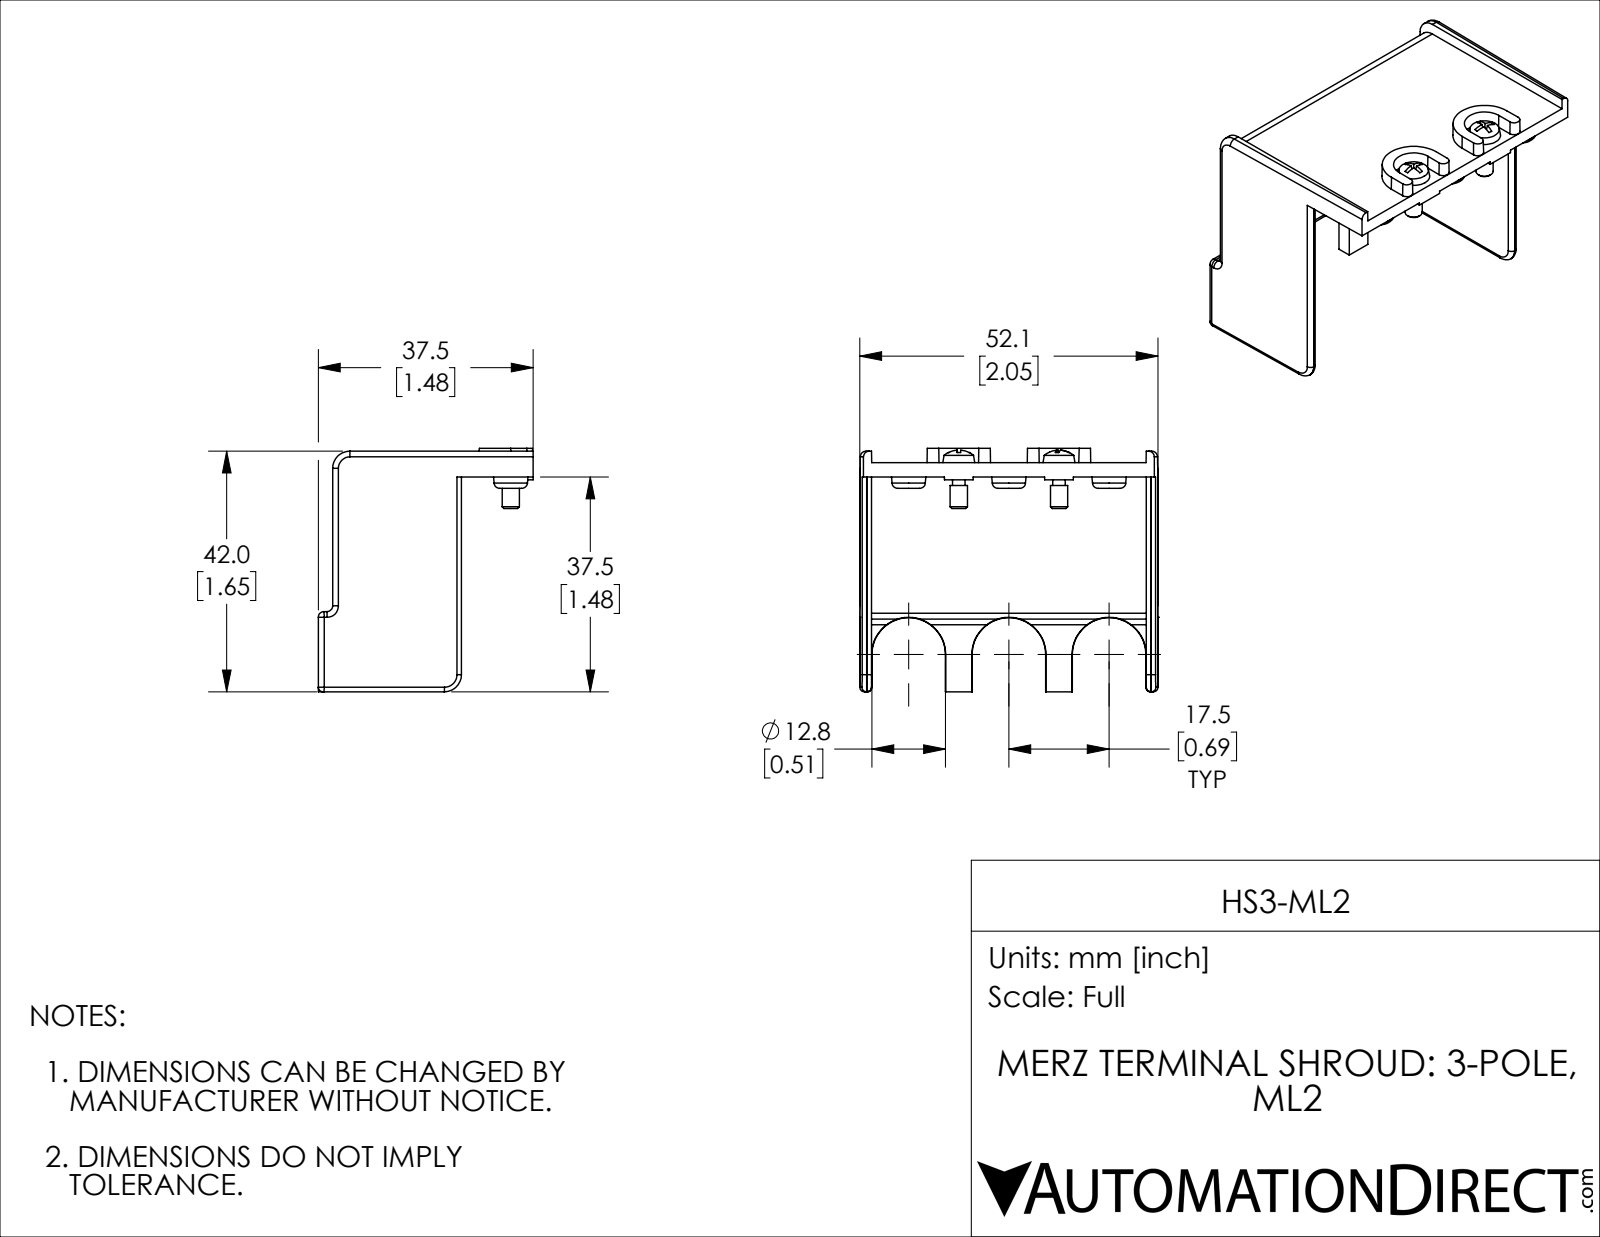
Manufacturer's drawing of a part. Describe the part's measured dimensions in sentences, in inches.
The part is named "HS3-ML2". Its 3-D file was written by "SolidWorks 2019 (AUTOMOTIVE_DESIGN)". It is 1 solid with 198 faces: 87 planar, 56 cylindrical and 55 other. Overall it measures 2.049 by 1.673 by 1.476 inches. Its volume is 0.679 cubic inches and its surface area 17.64 square inches. Round holes: 3 of diameter 0.118, 2 of diameter 0.091, 2 of diameter 0.126. Round bosses or shafts: 2 of diameter 0.118, 2 of diameter 0.086. Partial cylindrical surfaces (rounded edges, fillets, slot ends): 12 of radius 0.031, 12 of radius 0.039, 3 of radius 0.118. The main face-to-face distances are 0.098, 0.079, 1.89, 0.177, 1.476, 1.378, 1.299, 0.197, 0.689, 0.02. The hole center spacings are 0.344, 0.689, 1.033, 1.378.
